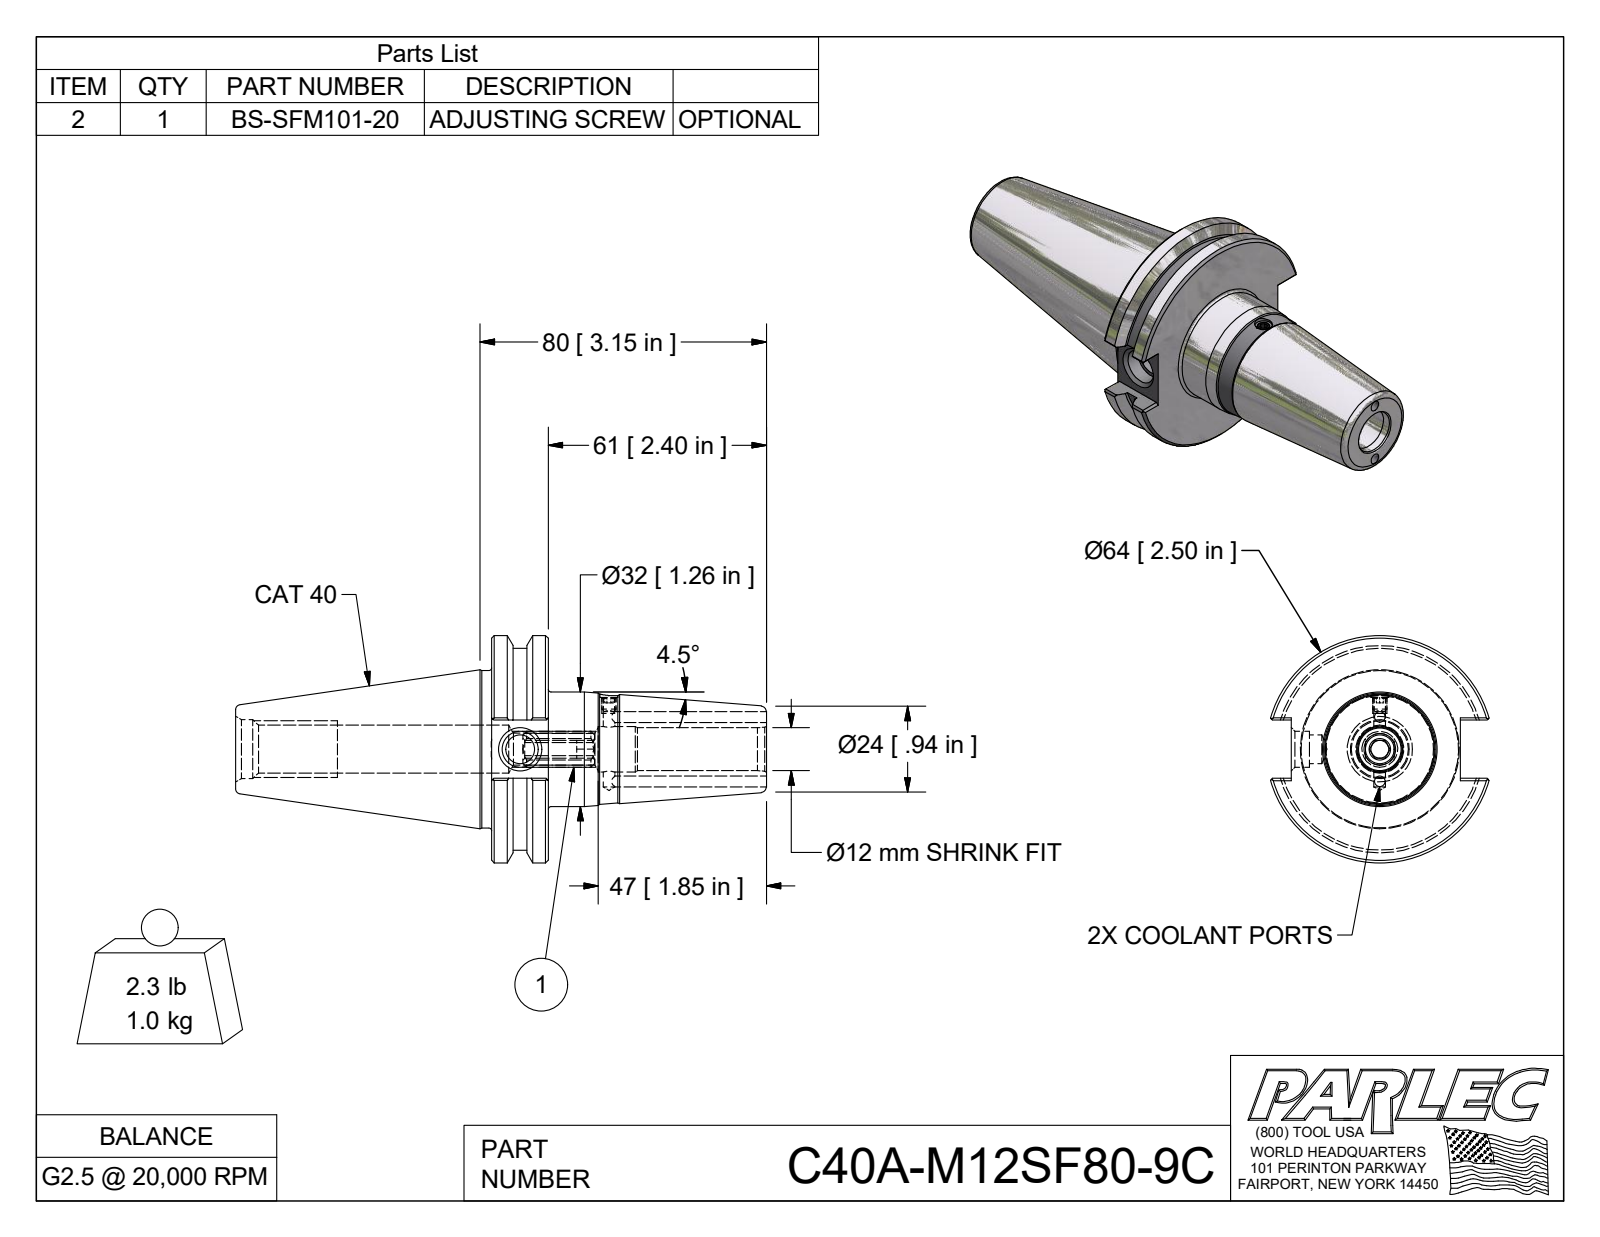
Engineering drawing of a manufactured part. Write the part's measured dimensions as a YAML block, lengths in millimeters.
part_name: "C40A-M12SF80-9C"
step_written_by: "Autodesk Inventor 2018 (AUTOMOTIVE_DESIGN)"
units: millimeters
bodies: {solids: 1, faces: 82, planar: 33, cylindrical: 20, other: 29}
overall_size: [148.26, 63.5, 61.05]
volume: 133590
surface_area: 28328
round_holes:
  - {diameter: 3, count: 2}
  - {diameter: 3.25, count: 1}
  - {diameter: 5, count: 1}
  - {diameter: 8, count: 1}
  - {diameter: 8.92, count: 1}
  - {diameter: 10.05, count: 1}
  - {diameter: 11.97, count: 1}
  - {diameter: 12.74, count: 1}
  - {diameter: 13.39, count: 1}
  - {diameter: 16.46, count: 1}
round_bosses_or_shafts:
  - {diameter: 63.5, count: 1}
  - {diameter: 56.36, count: 1}
  - {diameter: 43.94, count: 1}
  - {diameter: 32, count: 1}
face_to_face_distances: [15.88, 76.83, 60.95, 16.26, 47.25, 71.43, 87.31, 148.26, 81.31, 9.88]
hole_center_spacings: [9, 18]
